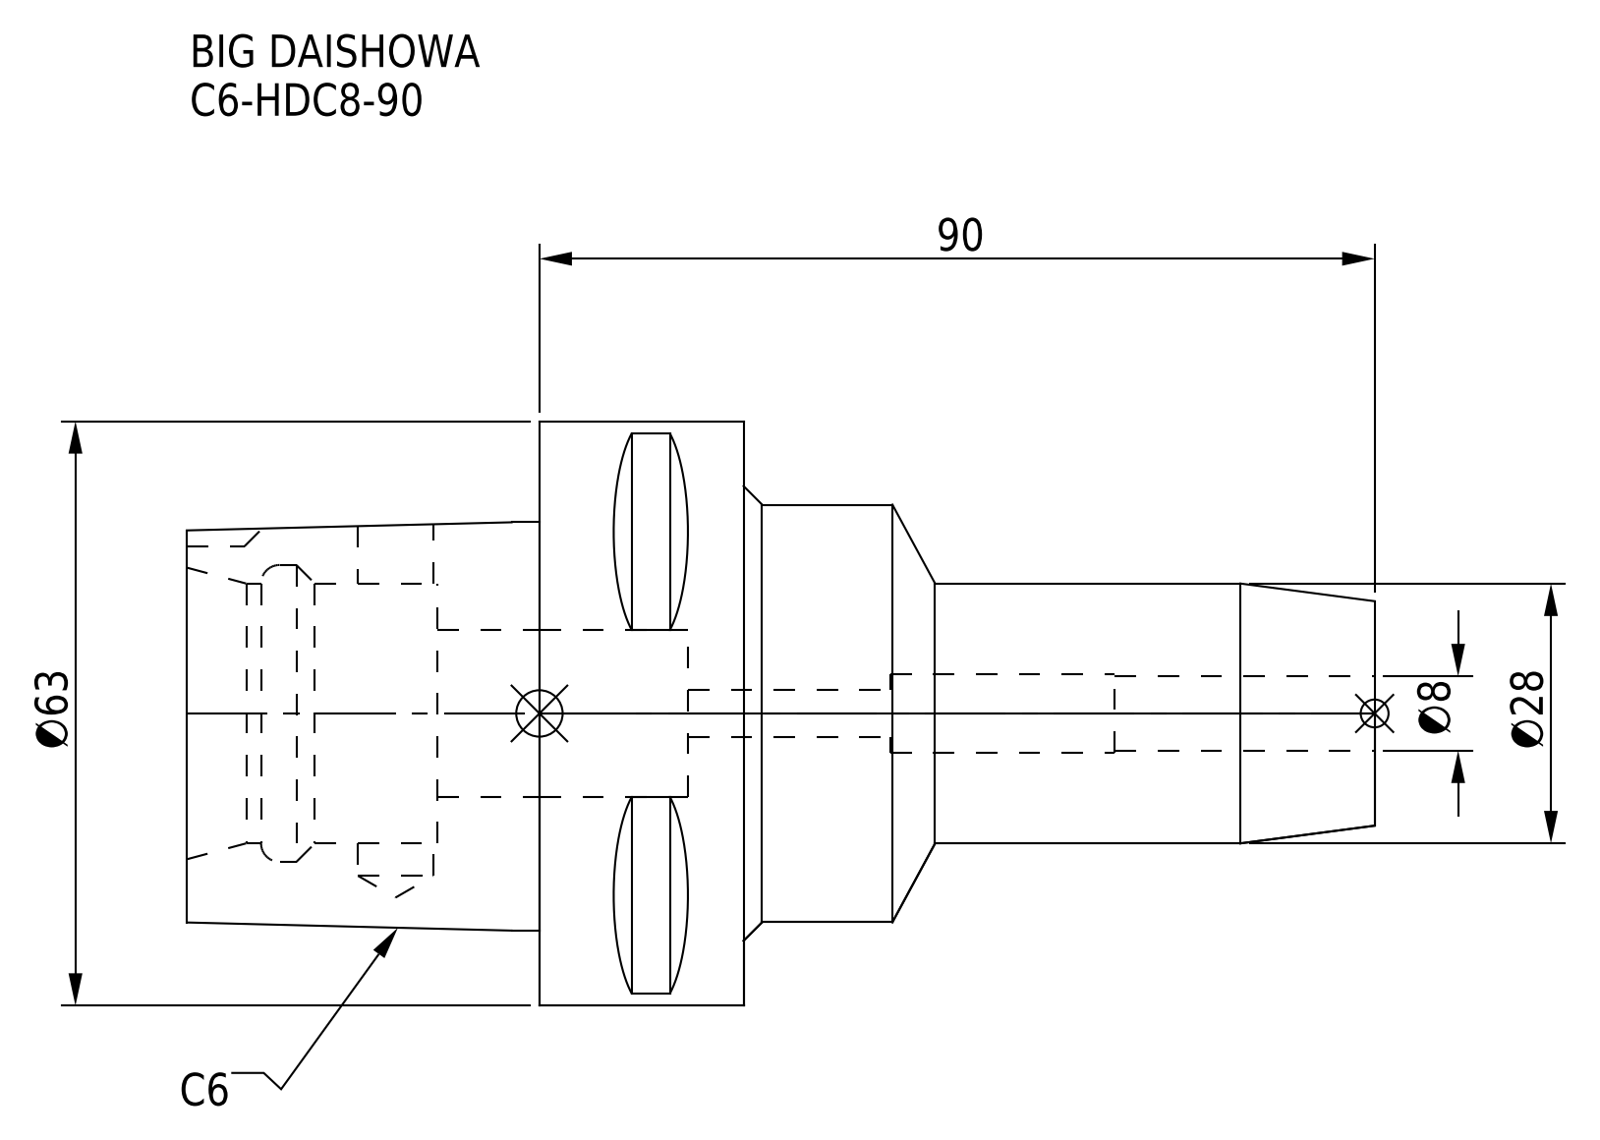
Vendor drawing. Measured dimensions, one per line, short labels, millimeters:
name: C6-HDC8-90
written by: CREO PARAMETRIC BY PTC INC, 2016380 (AUTOMOTIVE_DESIGN)
unit: mm
bodies: 1 solid, 71 faces (30 planar, 25 cylindrical, 16 other)
size: 128 × 63 × 63
volume: 152 081 mm³; area: 27 990 mm²
holes: 1× ⌀5, 1× ⌀8, 1× ⌀8.1, 1× ⌀8.5, 1× ⌀18, 1× ⌀28, 1× ⌀32
bosses: 1× ⌀63, 1× ⌀45
rounds: 1× R5
face distances: 22, 27, 60, 38, 68, 90, 128, 101, 33, 11
